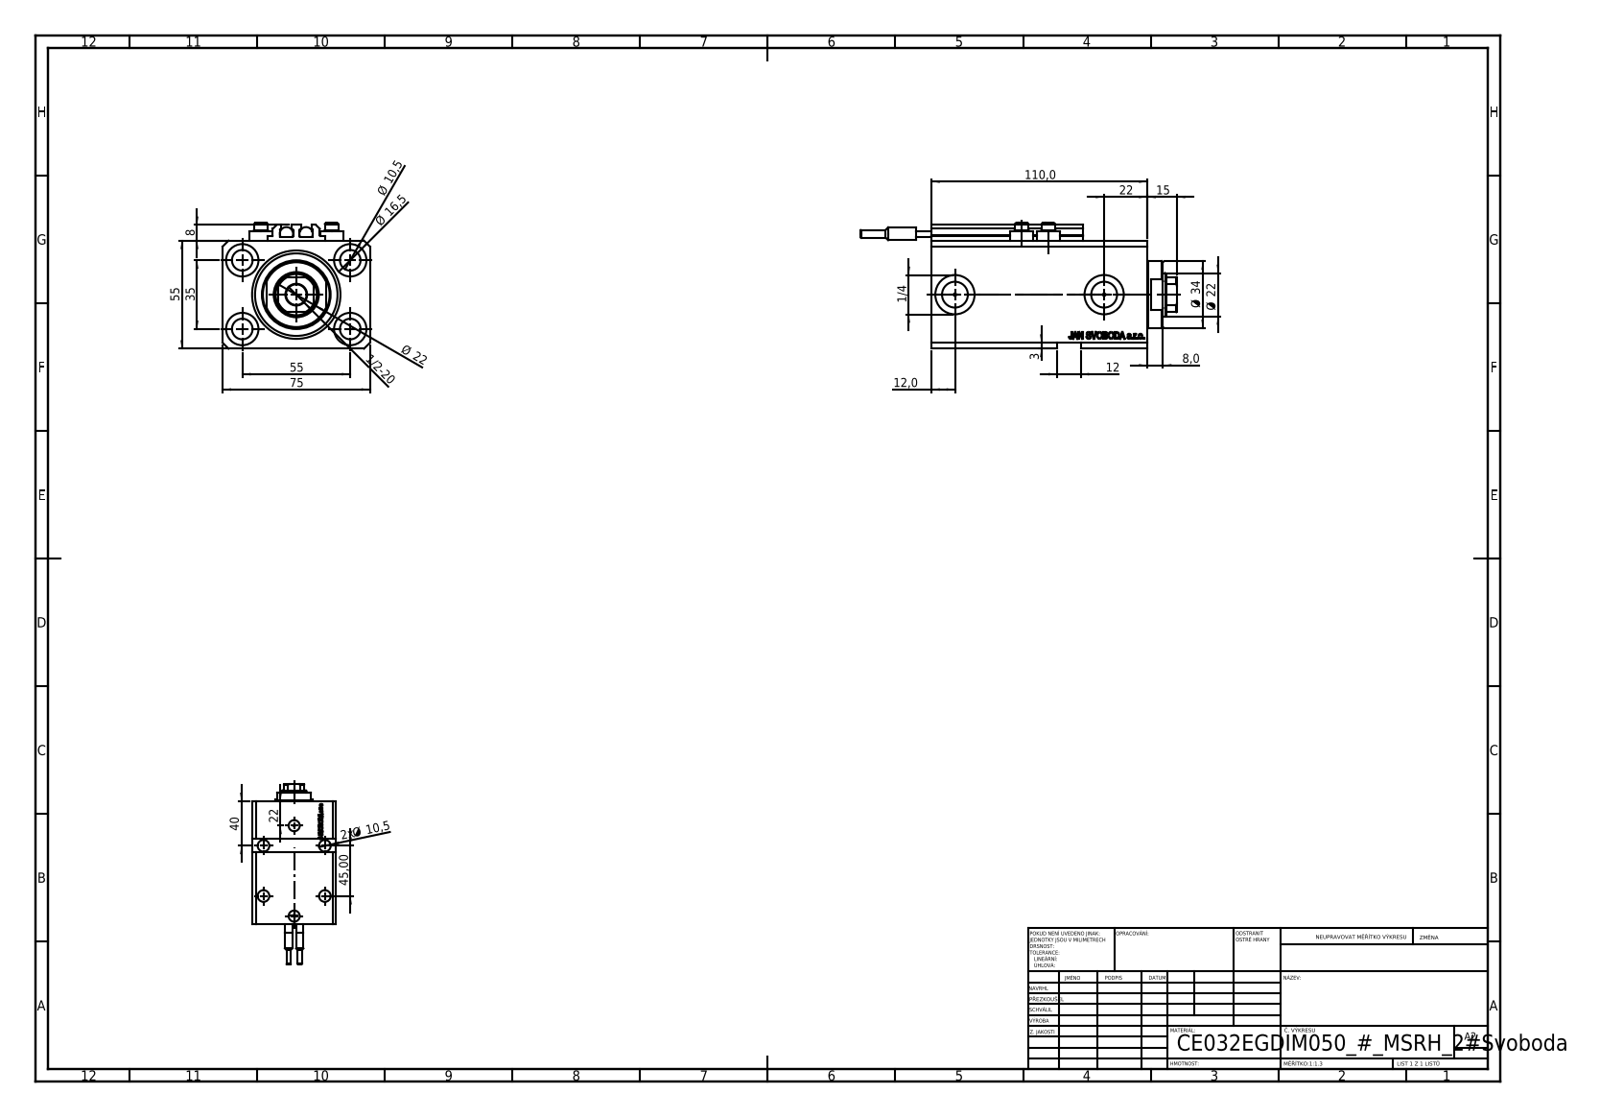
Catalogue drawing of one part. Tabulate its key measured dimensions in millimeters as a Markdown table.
| quantity | value |
| --- | --- |
| part name | V250CE_E_Body; SWITCH_V250CE; V250CE_VC_E; V250CE_C_VCP (+1 more) |
| STEP written by | SolidWorks 2019 (CONFIG_CONTROL_DESIGN) |
| units | millimeters |
| bodies | 10 solids, 1152 faces (550 planar, 170 cylindrical, 432 other) |
| overall size | 161 × 75 × 64 |
| volume | 381 291 mm³ |
| surface area | 99 541 mm² |
| round holes (diameter × count) | 10.5 × 9, 1.25 × 4, 4 × 4, 16.5 × 4, 10 × 2, 13.16 × 2, 20 × 2, 22 × 1, 32 × 1, 45 × 1 |
| round bosses / shafts (diameter × count) | 11.6 × 4, 7 × 4, 6.8 × 2, 6.5 × 2, 4 × 2, 34 × 1 |
| partial cylindrical surfaces (radius × count) | 0.2 × 10, 10.5 × 1 |
| main face-to-face distances | 55, 75, 3, 15, 110, 57, 95, 9.9, 85.1, 100.1 |
| hole center spacings | 32.6, 32.87, 55, 68.74, 13.6, 14.09, 23.05, 25.81 |
